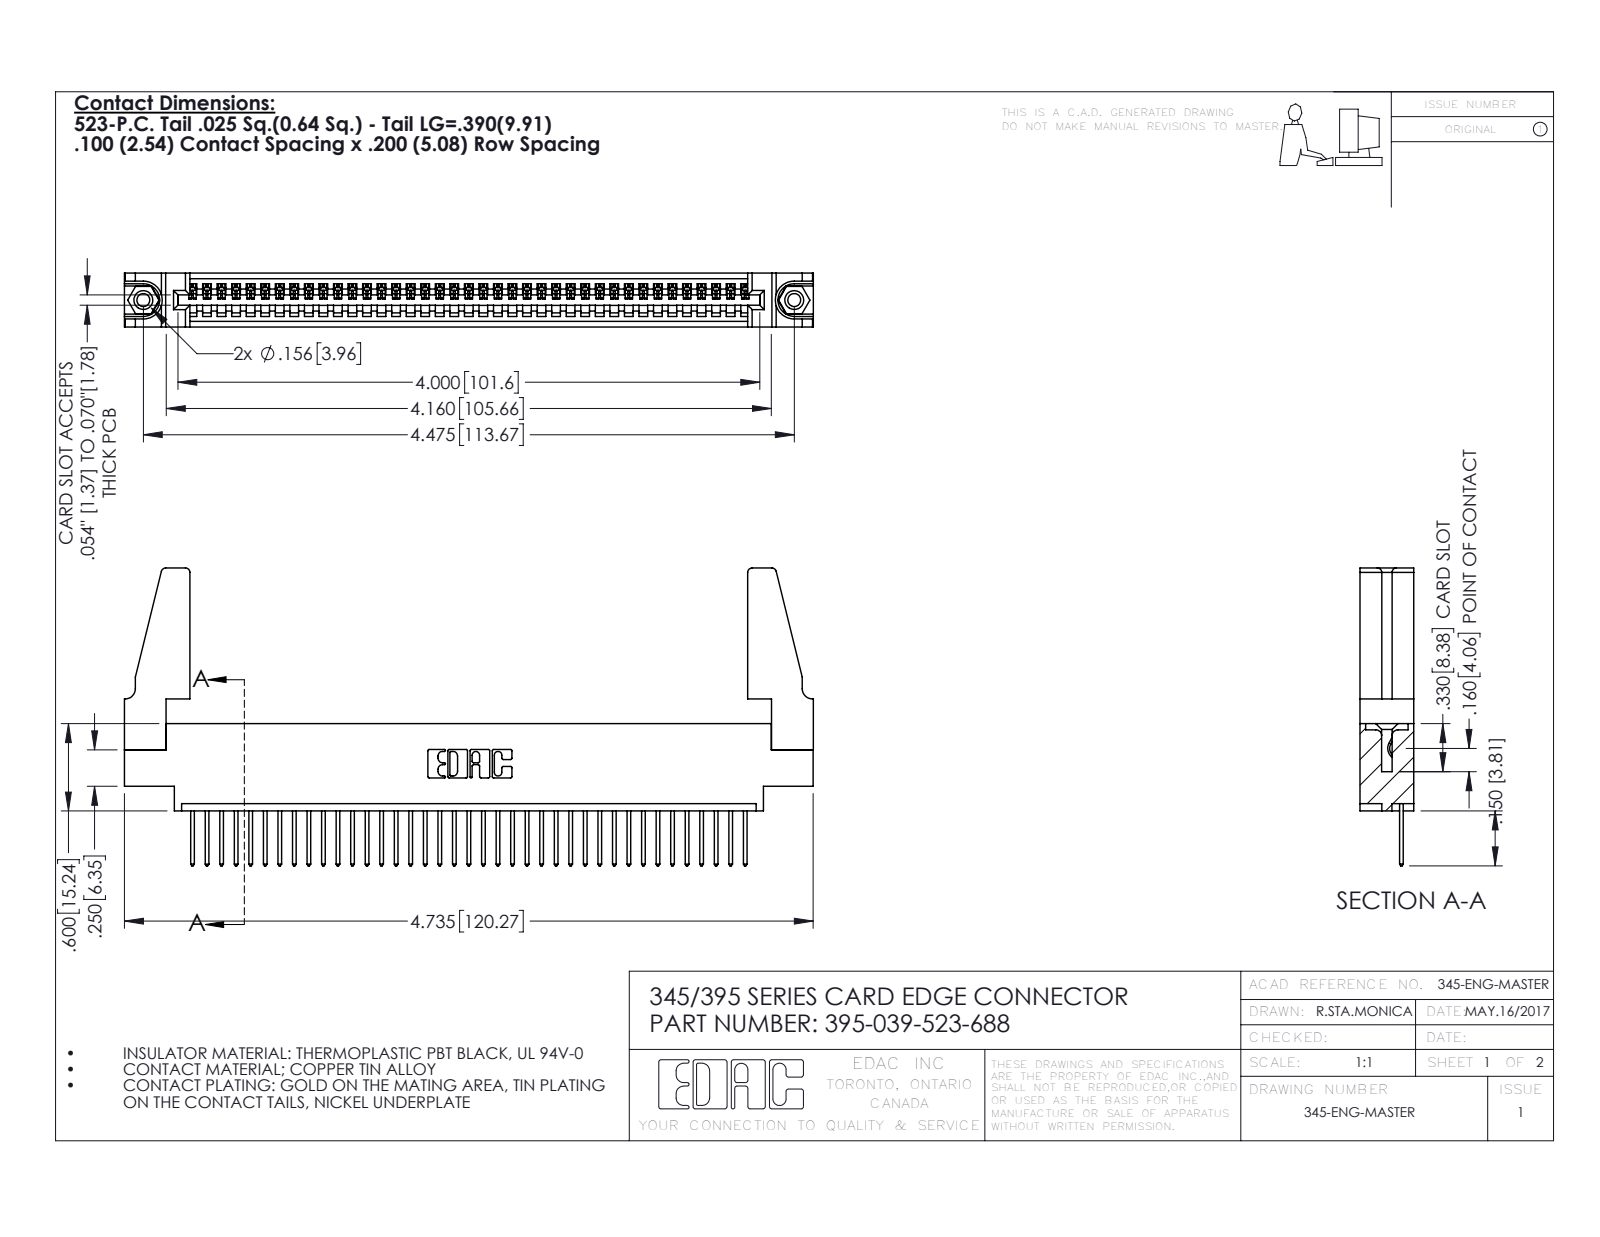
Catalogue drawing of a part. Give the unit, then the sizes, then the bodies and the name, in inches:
Units: inches
Overall size (bounding box): 4.736 × 2.047 × 0.37
Round holes (diameter × count): ⌀0.089 ×2, ⌀0.125 ×2, ⌀0.156 ×2, ⌀0.064 ×1
Round bosses / shafts (diameter × count): ⌀0.155 ×2
Partial cylindrical surfaces — rounded edges, fillets, slot ends (radius × count): R0.006 ×78, R0.01 ×78, R0.01 ×22, R0.03 ×8, R0.007 ×6, R0.031 ×6, R0.026 ×3, R0.031 ×2
Main face-to-face distances: 0.072, 0.37, 0.298, 0.098, 0.272, 0.025, 0.2, 0.225, 0.175, 0.149
Hole centre spacings: 0.27, 4.239, 4.475
Volume: 0.886 in³ · Surface area: 28.27 in²
Bodies: 44 solids, 2516 faces (1716 planar, 784 cylindrical, 16 other)
Part name (STEP PRODUCT): 395-039-523-688; 345-292-001_345-293-123; 345 Part_0.170 Offset - 0.156 Dia-TH; 345-220-078_345-220-088 (+1 more)
STEP written by: SolidWorks 2016 (CONFIG_CONTROL_DESIGN)
